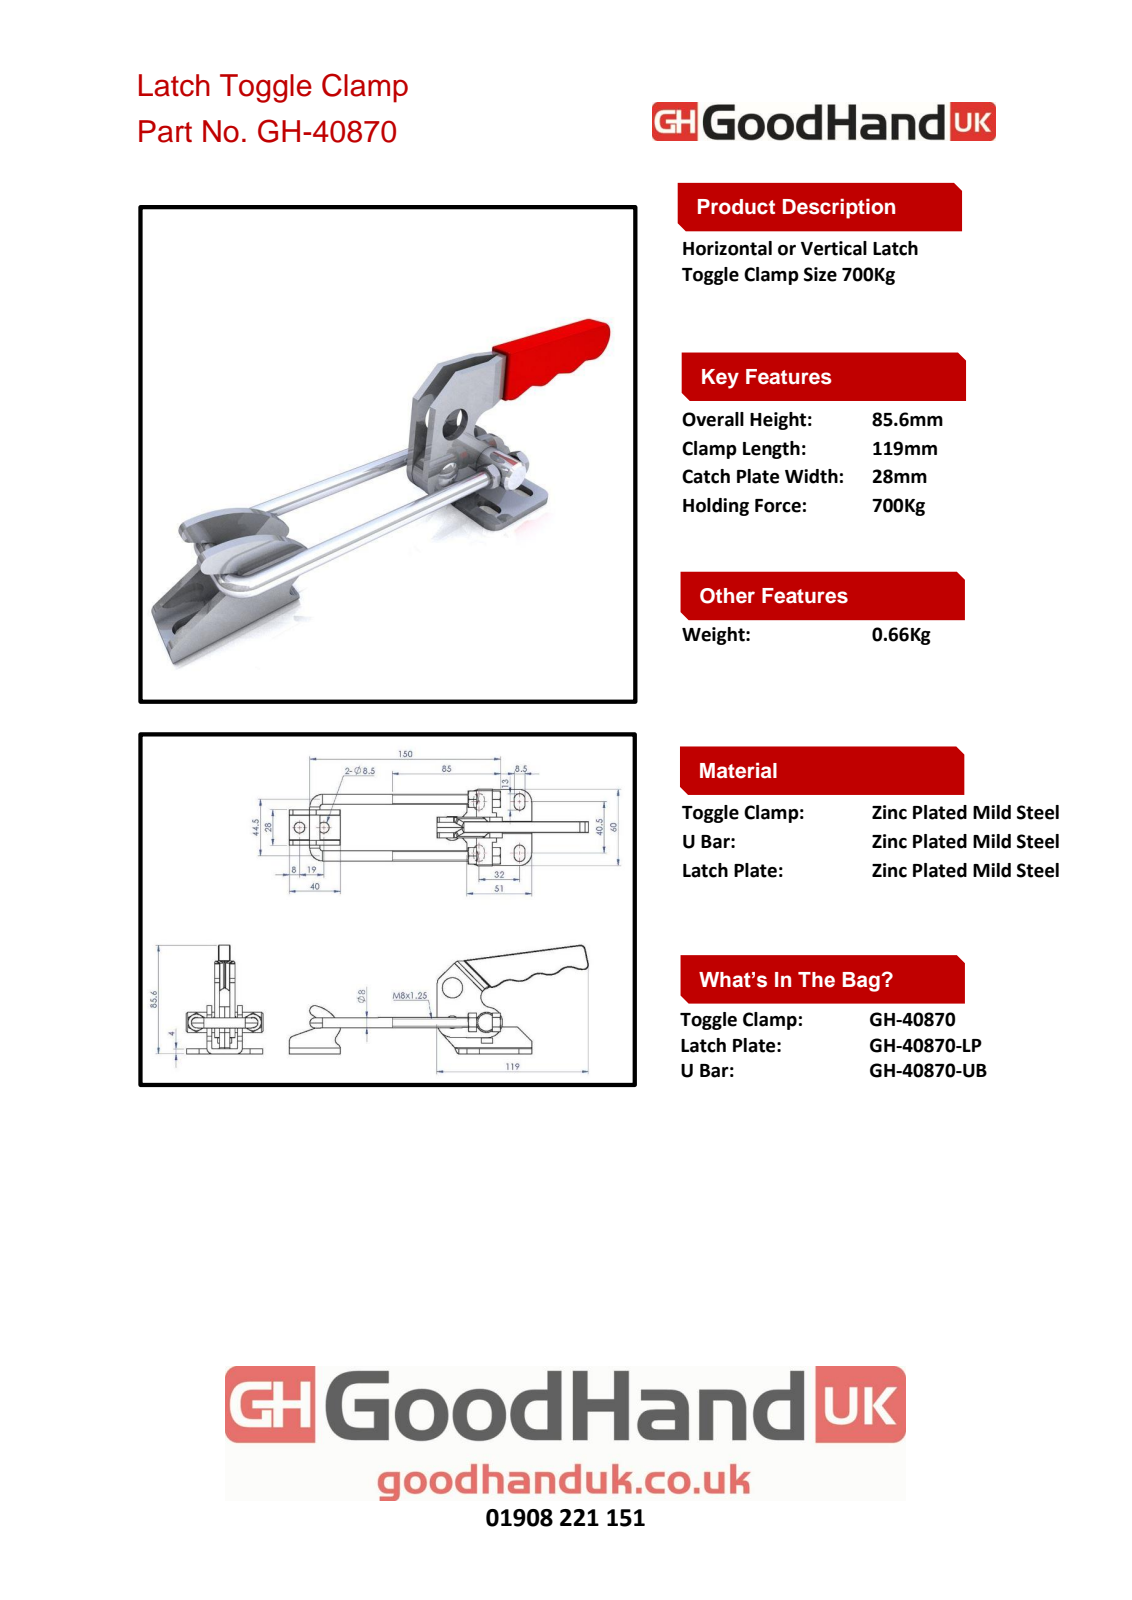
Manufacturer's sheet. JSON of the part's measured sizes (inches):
{"part_name": "Group2^GH-40870(簡化); Group1^GH-40870(簡化); GH-40870(簡化); 44087044-1^GH-40870(簡化) (+2 more)", "step_written_by": "SolidWorks 2016 (AUTOMOTIVE_DESIGN)", "units": "inches", "bodies": {"solids": 7, "faces": 452, "planar": 126, "cylindrical": 168, "other": 158}, "overall_size": [9.254, 3.37, 2.374], "volume_in3": 5.569, "surface_area_in2": 72.05, "round_holes": [[0.315, 5], [0.268, 2], [0.335, 2], [0.63, 2], [0.236, 1]], "round_bosses_or_shafts": [[0.315, 2]], "partial_cylinders_radius": [[0.167, 8], [0.197, 7], [0.02, 6], [0.177, 6], [0.157, 4], [0.325, 4], [0.394, 4], [0.443, 3]], "face_to_face_distances": [0.157, 0.473, 0.709, 0.236, 0.346, 0.354, 0.031, 0.315, 0.323, 0.126], "hole_center_spacings": [1.752, 1.063, 0.748, 1.503, 4.252, 4.396, 5.315]}
